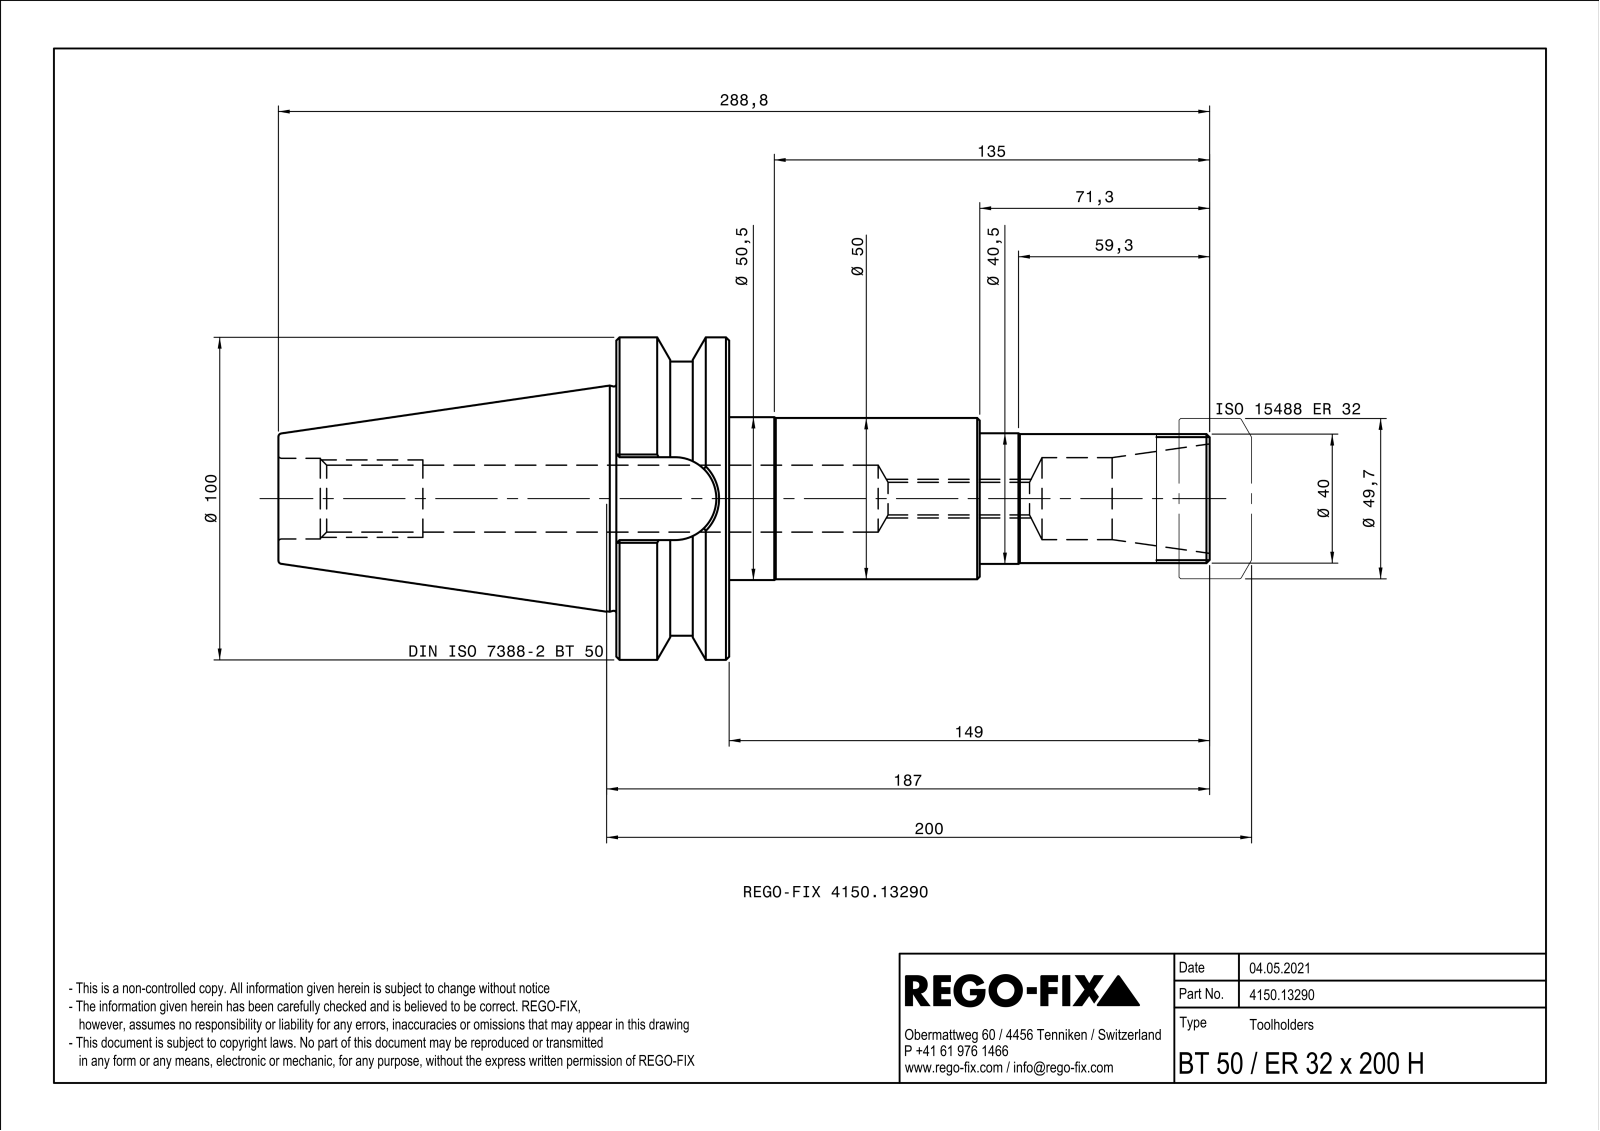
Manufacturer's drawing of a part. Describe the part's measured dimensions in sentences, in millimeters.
The part is named "NOCUT". Its 3-D file was written by "SIEMENS PLM Software Solid Edge ST10 (AUTOMOTIVE_DESIGN)". It is 2 solids with 202 faces: 57 planar, 49 cylindrical and 96 other. Overall it measures 289.2 by 100.3 by 100.3 millimeters. Its volume is 1 286 000 cubic millimeters and its surface area 167 216 square millimeters. Round holes: 1 of diameter 10.11, 1 of diameter 20.75, 1 of diameter 23.5, 1 of diameter 24.7, 1 of diameter 25. Round bosses or shafts: 1 of diameter 100.3, 1 of diameter 100, 1 of diameter 85, 1 of diameter 50.8, 1 of diameter 50.5, 1 of diameter 50.3, 1 of diameter 50, 1 of diameter 40.8. Partial cylindrical surfaces (rounded edges, fillets, slot ends): 4 of radius 0.5, 1 of radius 12.85. The main face-to-face distances are 35, 35.2, 70.7, 140, 25.7, 77.7, 217.7, 149, 289, 140.2.
